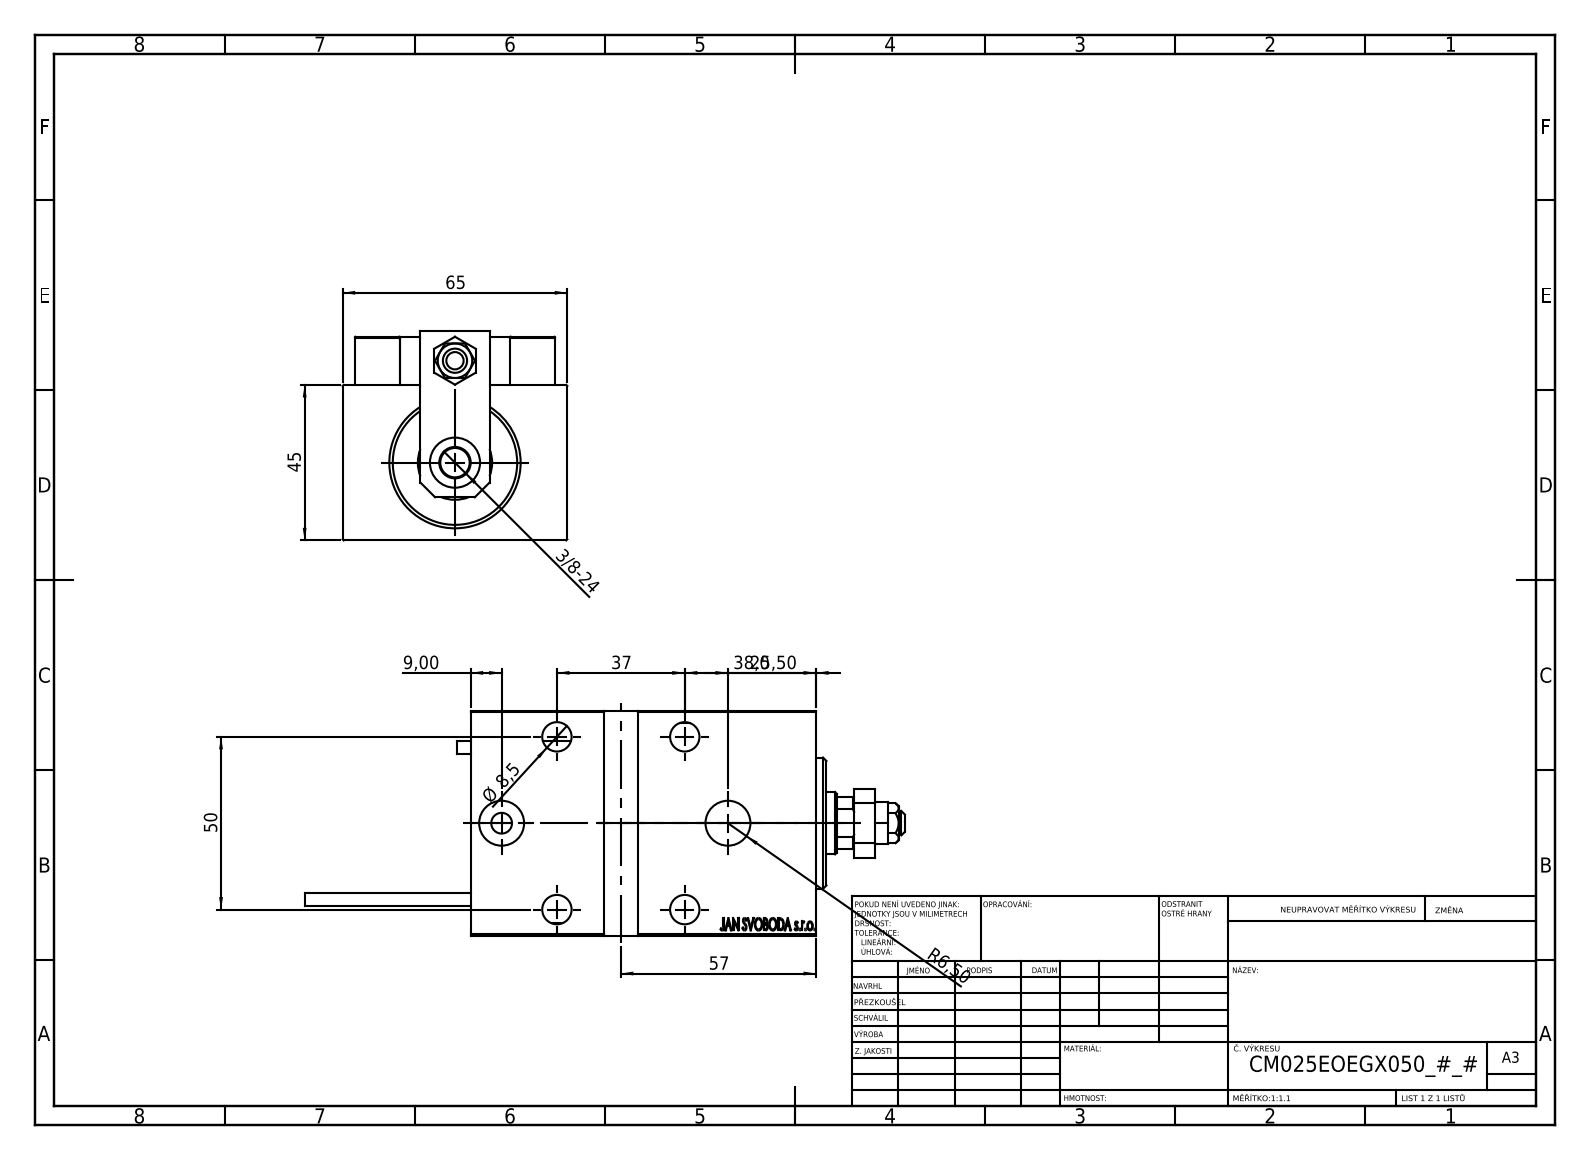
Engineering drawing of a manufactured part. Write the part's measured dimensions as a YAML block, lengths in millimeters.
part_name: "V450CM_E_VCP; ZARAZKA; Block; NUT_D12 (+7 more)"
step_written_by: "SolidWorks 2019 (CONFIG_CONTROL_DESIGN)"
units: millimeters
bodies: {solids: 24, faces: 1286, planar: 569, cylindrical: 176, other: 541}
overall_size: [173.7, 65, 60.5]
volume: 317688
surface_area: 77608
round_holes:
  - {diameter: 8, count: 5}
  - {diameter: 8.5, count: 5}
  - {diameter: 3.2, count: 4}
  - {diameter: 4, count: 4}
  - {diameter: 13.5, count: 4}
  - {diameter: 5, count: 2}
  - {diameter: 13, count: 2}
  - {diameter: 7, count: 1}
  - {diameter: 14.5, count: 1}
  - {diameter: 18, count: 1}
  - {diameter: 21.5, count: 1}
  - {diameter: 25, count: 1}
round_bosses_or_shafts:
  - {diameter: 5, count: 2}
  - {diameter: 3.8, count: 2}
  - {diameter: 38, count: 1}
  - {diameter: 27, count: 1}
  - {diameter: 13, count: 1}
  - {diameter: 11, count: 1}
  - {diameter: 6, count: 1}
partial_cylinders:
  - {radius: 0.3, count: 30}
  - {radius: 3, count: 2}
  - {radius: 8.5, count: 1}
face_to_face_distances: [45, 65, 14, 59, 6, 100, 13, 111, 10, 5]
hole_center_spacings: [40.31, 10.77, 11.37, 20, 21.03, 25, 27.95, 29.59]
